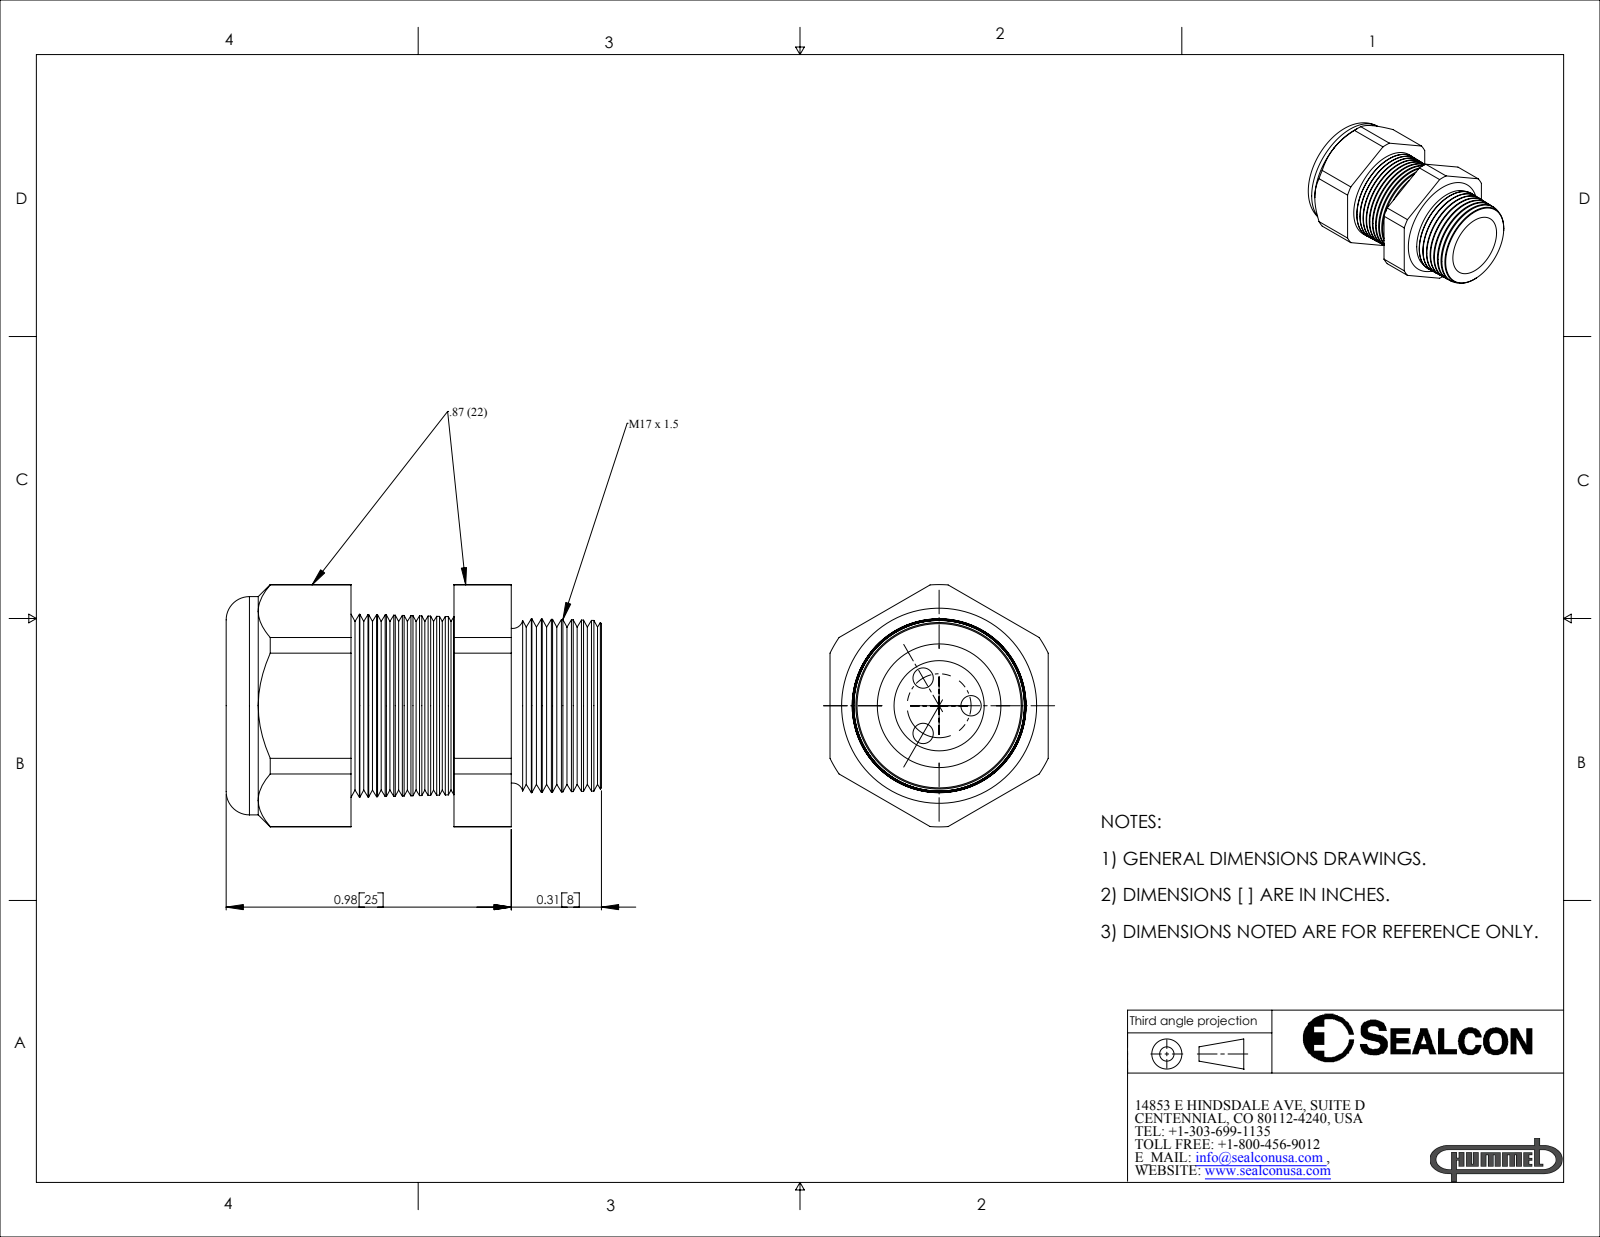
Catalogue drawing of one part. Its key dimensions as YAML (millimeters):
part_name: "CD17M4-BK"
step_written_by: "SolidWorks 2007 (CONFIG_CONTROL_DESIGN)"
units: millimeters
bodies: {solids: 2, faces: 185, planar: 21, cylindrical: 26, other: 138}
overall_size: [32.8, 21.2, 19.1]
volume: 5820
surface_area: 4298
round_holes:
  - {diameter: 1.8, count: 3}
  - {diameter: 7.4, count: 1}
  - {diameter: 7.9, count: 1}
round_bosses_or_shafts:
  - {diameter: 19.1, count: 1}
partial_cylinders:
  - {radius: 10.6, count: 1}
face_to_face_distances: [19.1, 19.1, 19.9, 10.9, 9, 24.9, 14, 5, 32.8, 21.9]
hole_center_spacings: [4.9, 2.8, 2.8]
